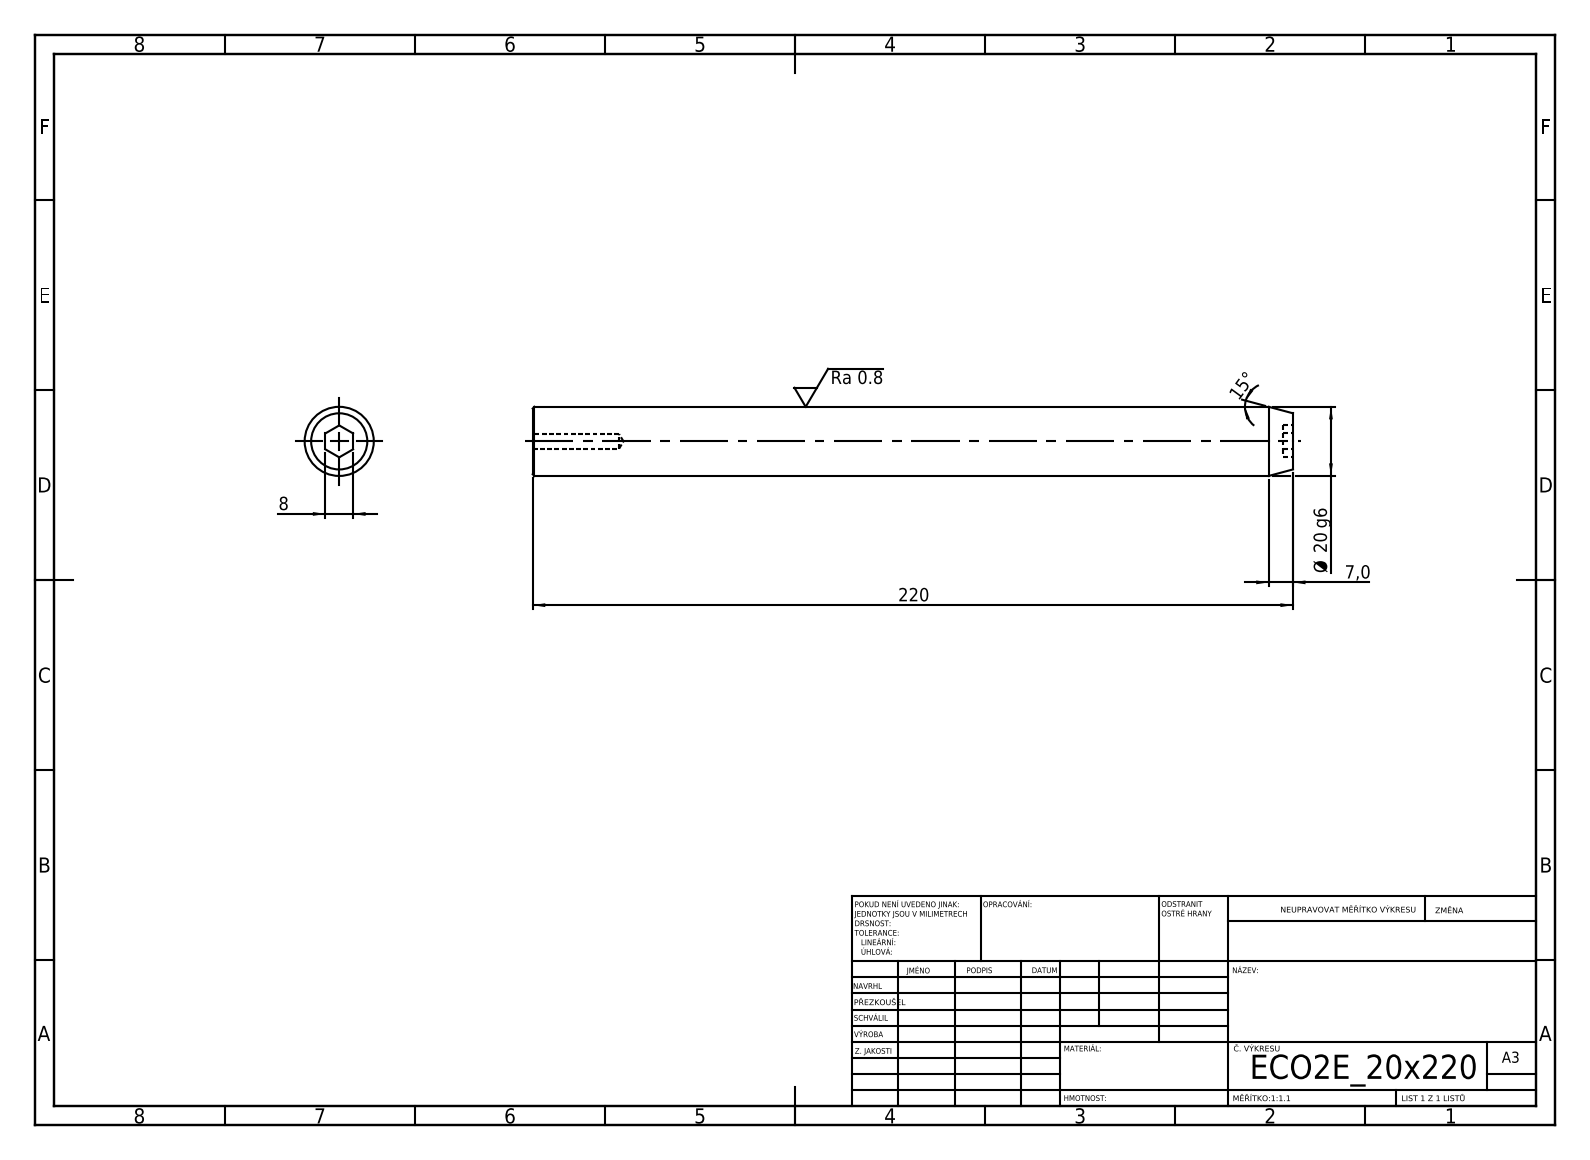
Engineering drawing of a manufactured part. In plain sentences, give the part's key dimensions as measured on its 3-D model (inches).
Its 3-D file was written by "SolidWorks 2019 (CONFIG_CONTROL_DESIGN)". It is 1 solid with 19 faces: 9 planar, 4 cylindrical and 6 other. Overall it measures 8.661 by 0.787 by 0.787 inches. Its volume is 4.163 cubic inches and its surface area 22.8 square inches. Round holes: 1 of diameter 0.165. Round bosses or shafts: 1 of diameter 0.787. The main face-to-face distances are 8.661, 0.11, 8.551, 0.315.
